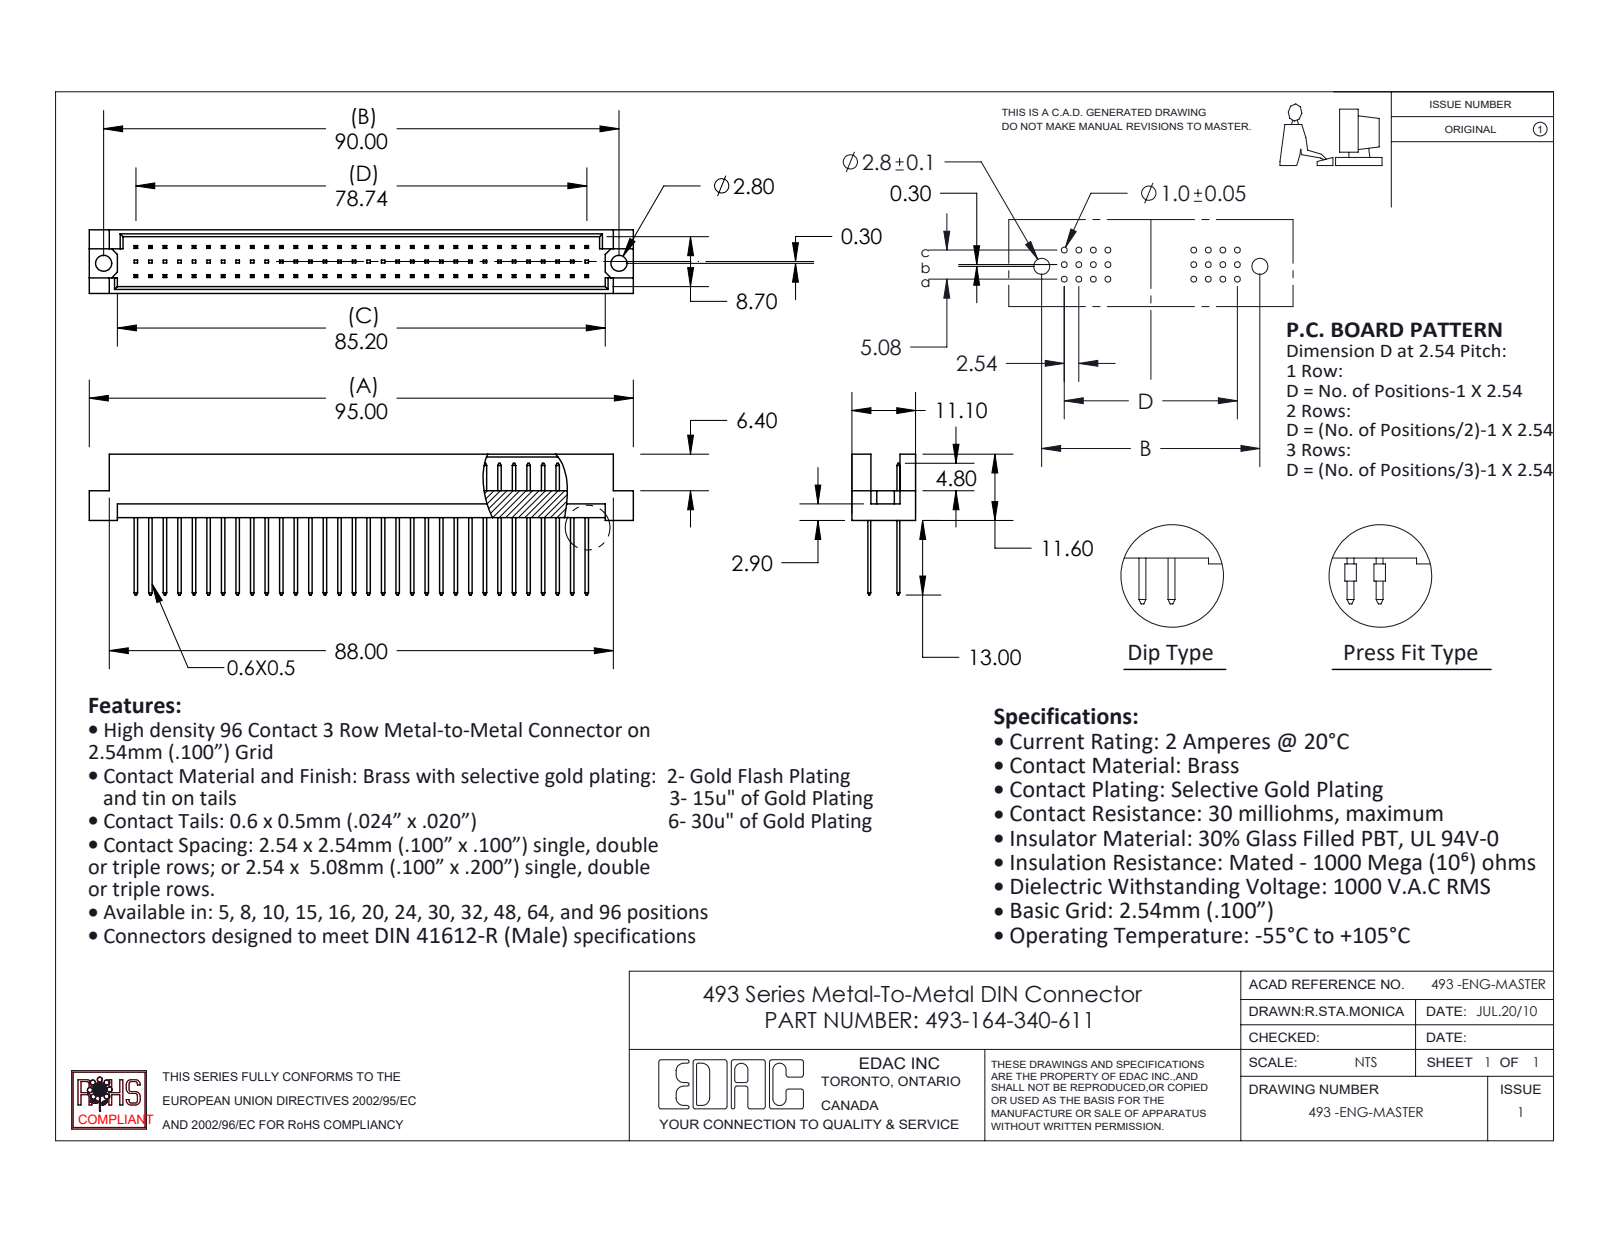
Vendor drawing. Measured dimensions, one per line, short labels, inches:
name: 493 Part_96; 493-164-340-611; 493-290_40
written by: SolidWorks 2020 (CONFIG_CONTROL_DESIGN)
unit: in
bodies: 65 solids, 1332 faces (1328 planar, 4 cylindrical, 0 other)
size: 3.74 × 0.969 × 0.437
volume: 0.372 in³; area: 15.02 in²
holes: 2× ⌀0.11
face distances: 0.2, 0.047, 0.39, 0.02, 0.109, 0.128, 0.309, 0.328, 0.061, 0.081
hole spacings: 3.543
